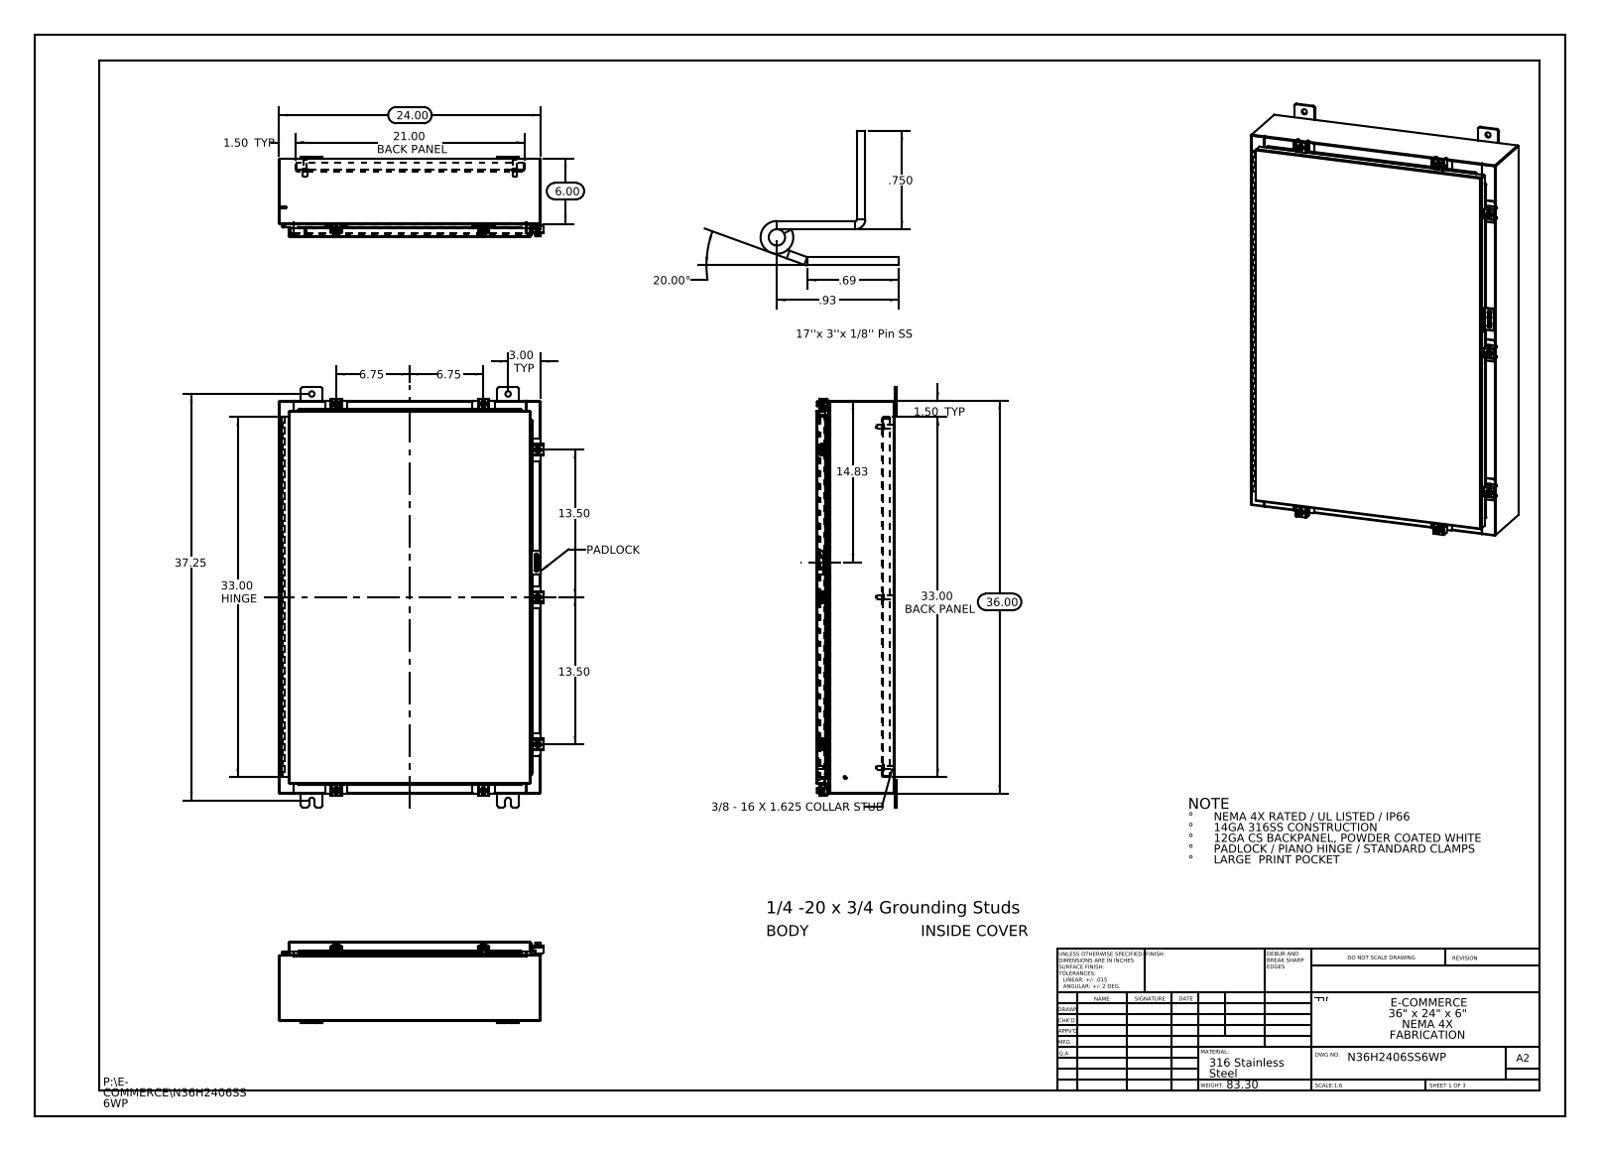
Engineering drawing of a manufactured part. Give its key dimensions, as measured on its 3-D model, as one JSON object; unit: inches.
{"part_name": "N36H2406SS6WP Body; N36H2406SS6WP Mounting Feet; N36H2406SS6WP 22104005_DEFAULT; N36H2406SS6WP Top (+8 more)", "step_written_by": "SolidWorks 2013 (CONFIG_CONTROL_DESIGN)", "units": "inches", "bodies": {"solids": 56, "faces": 2210, "planar": 1144, "cylindrical": 930, "other": 136}, "overall_size": [38.5, 24.211, 7.389], "volume_in3": 292.8, "surface_area_in2": 7269, "round_holes": [[0.5, 10], [0.213, 7], [0.26, 7], [0.125, 2], [0.125, 1]], "round_bosses_or_shafts": [[0.25, 8], [0.5, 7], [0.399, 7], [0.625, 6], [0.375, 6], [0.33, 6], [0.315, 2], [0.236, 2]], "partial_cylinders_radius": [[0.06, 34], [0.013, 27], [0.19, 24], [0.088, 21], [0.12, 14], [0.141, 14], [0.05, 11], [0.08, 10]], "face_to_face_distances": [0.075, 7.126, 7.051, 7.201, 0.104, 1, 1.075, 6.051, 6.126, 1.179], "hole_center_spacings": [13.5, 15.625, 17.957, 24.793, 33.474, 37.154, 19.25, 1.858]}
